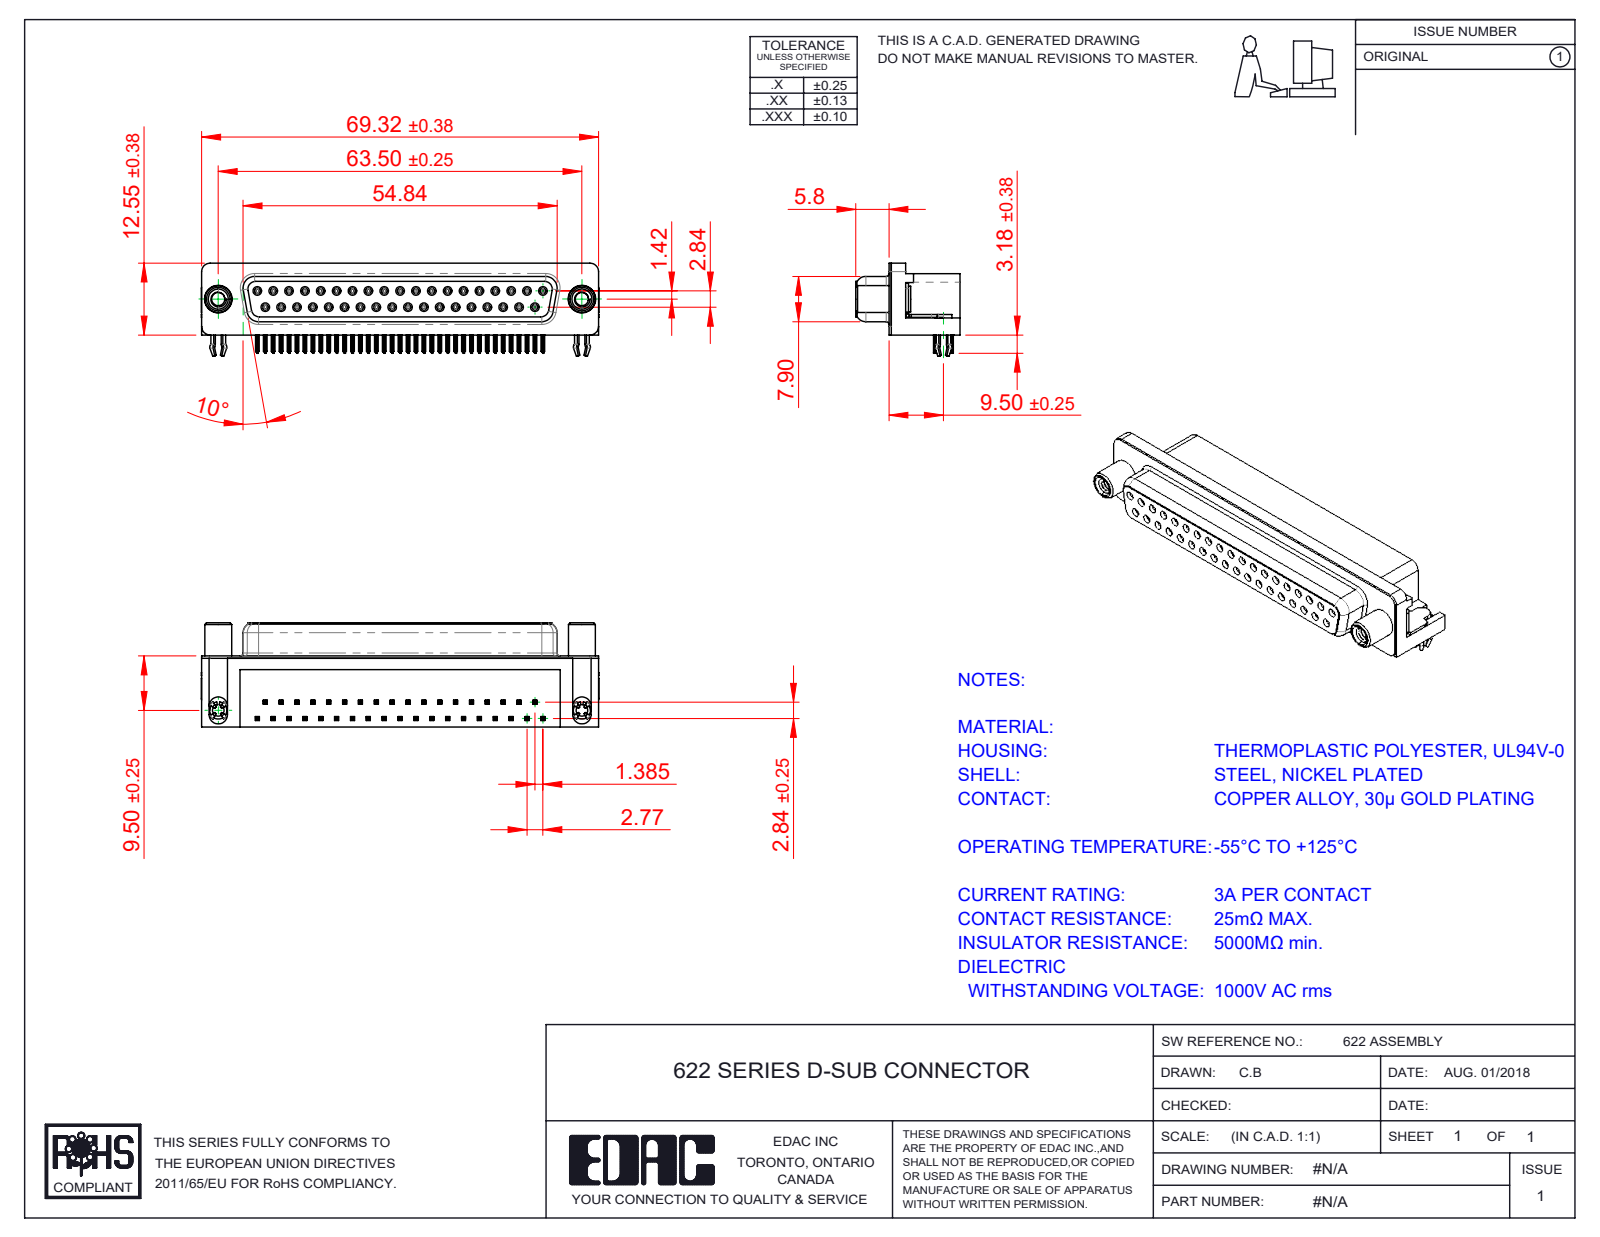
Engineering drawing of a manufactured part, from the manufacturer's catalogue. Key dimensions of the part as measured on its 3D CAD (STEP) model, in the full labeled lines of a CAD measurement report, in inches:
Part name (STEP PRODUCT): 622 Round Threaded Standoff; 622-037-668-550; 622 Contact Top; 622 4-40 Threaded Board Mount (+3 more)
STEP written by: SolidWorks 2016 (CONFIG_CONTROL_DESIGN)
Units: inches
Bodies: 43 solids, 5586 faces (2496 planar, 1318 cylindrical, 1772 other)
Overall size (bounding box): 2.732 × 0.717 × 0.619
Volume: 0.644 in³ · Surface area: 20.09 in²
Round holes (diameter × count): ⌀0.031 ×37, ⌀0.035 ×37, ⌀0.089 ×2, ⌀0.091 ×2, ⌀0.122 ×2, ⌀0.157 ×2, ⌀0.189 ×2, ⌀0.197 ×2
Round bosses / shafts (diameter × count): ⌀0.047 ×37, ⌀0.193 ×2, ⌀0.185 ×2, ⌀0.177 ×2, ⌀0.152 ×2, ⌀0.128 ×2
Partial cylindrical surfaces — rounded edges, fillets, slot ends (radius × count): R0.004 ×296, R0.006 ×148, R0.014 ×74, R0.013 ×37, R0.011 ×18, R0.039 ×18, R0.053 ×8, R0.063 ×8
Main face-to-face distances: 0.016, 0.472, 0.244, 0.407, 0.033, 0.262, 0.018, 0.112, 0.114, 0.278
Hole centre spacings: 0.124, 0.109, 0.218, 0.327, 0.436, 0.872, 0.545, 0.763
